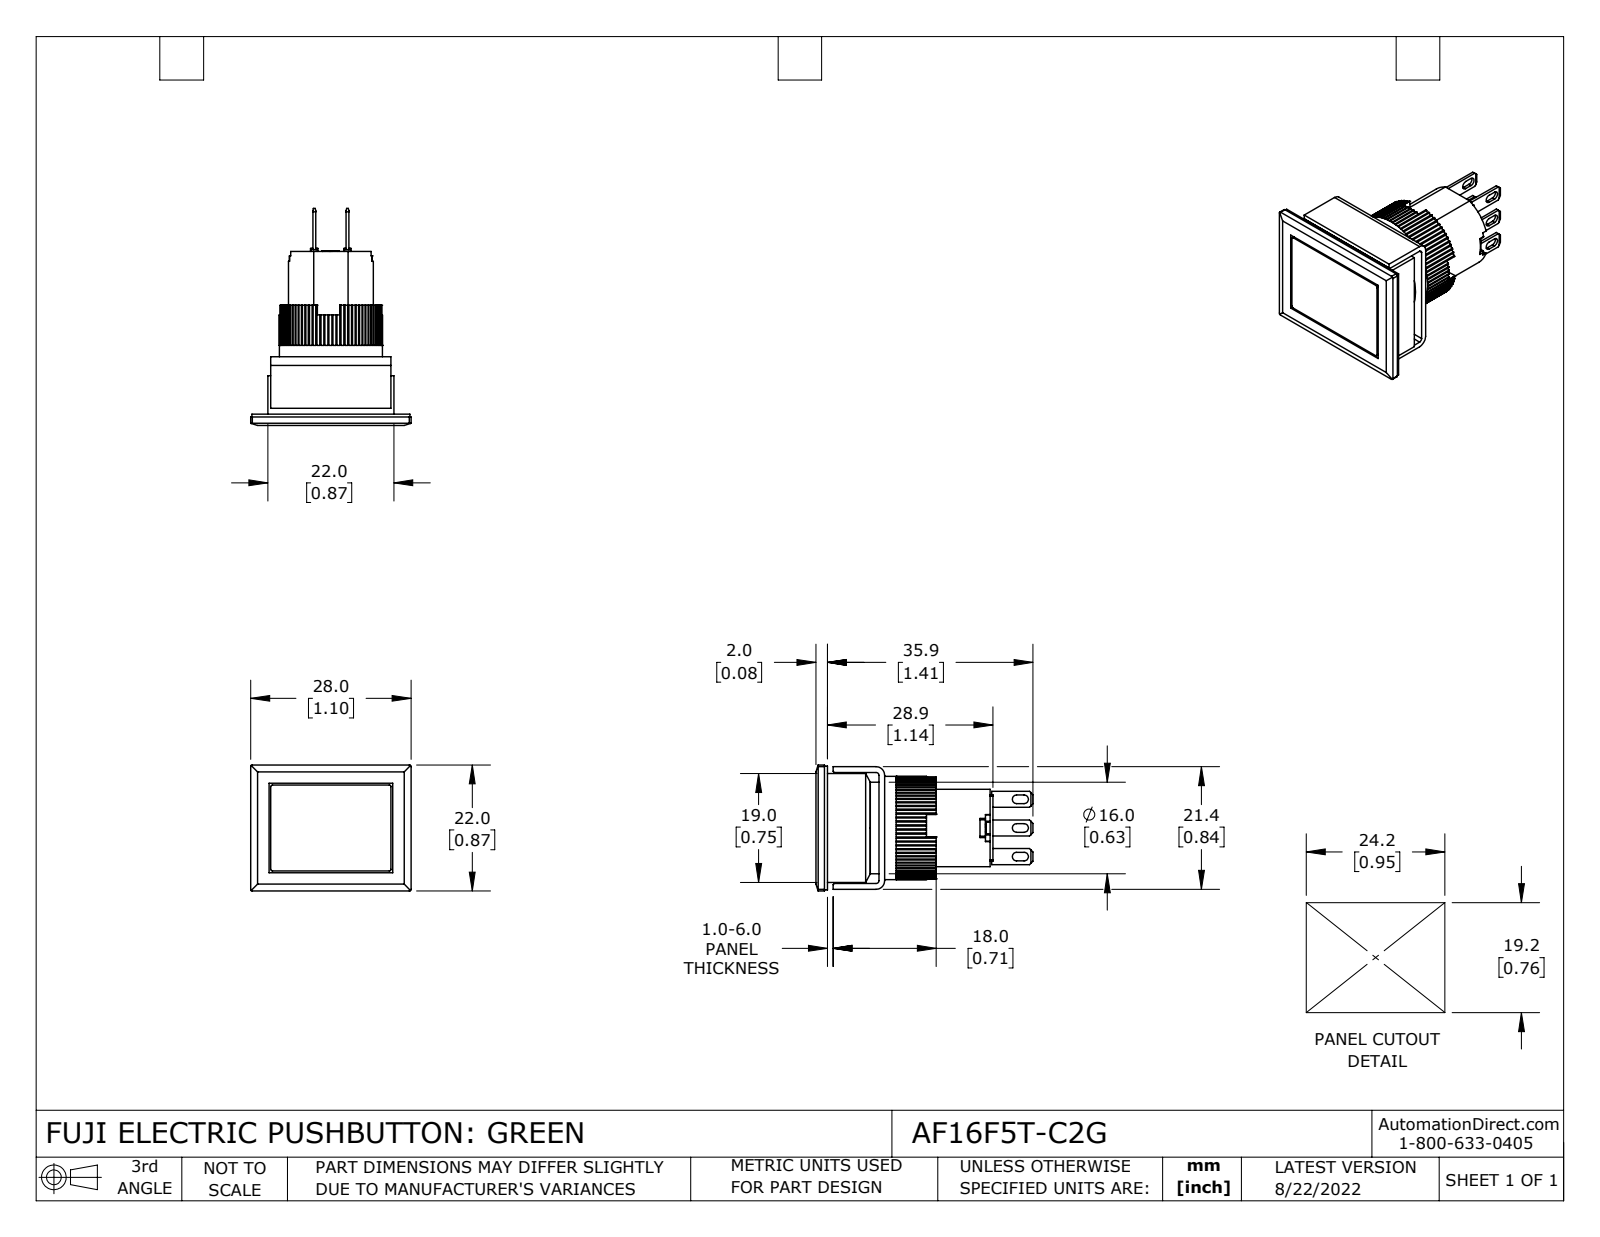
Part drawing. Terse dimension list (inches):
name: AF16F5T-C2G
written by: SolidWorks 2021 (CONFIG_CONTROL_DESIGN)
unit: in
bodies: 12 solids, 798 faces (620 planar, 176 cylindrical, 2 other)
size: 1.492 × 1.102 × 0.866
volume: 0.541 in³; area: 11.85 in²
holes: 1× ⌀0.039, 1× ⌀0.709
bosses: 1× ⌀0.63, 1× ⌀0.583
rounds: 80× R0.01, 12× R0.008, 8× R0.012, 6× R0.03, 2× R0.02, 2× R0.059
face distances: 0.374, 0.059, 0.02, 0.142, 0.039, 0.315, 0.232, 0.083, 0.079, 0.756
